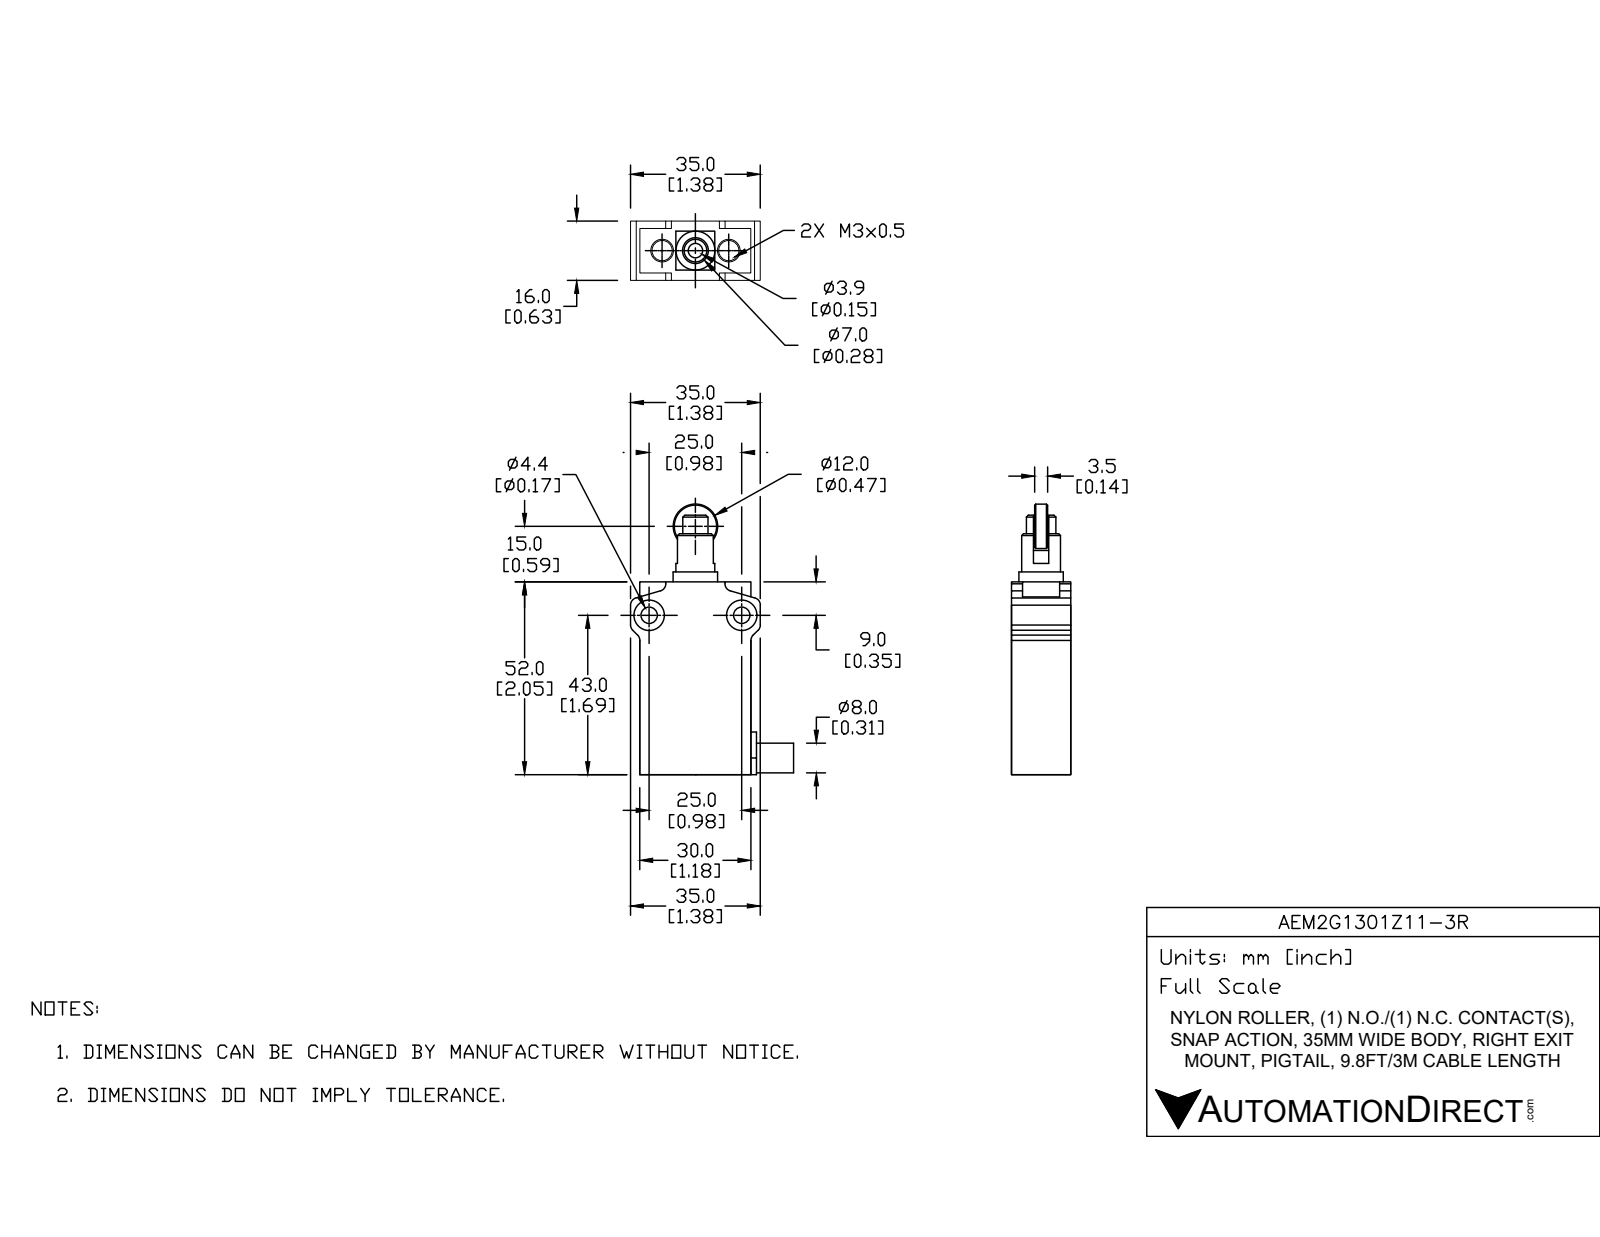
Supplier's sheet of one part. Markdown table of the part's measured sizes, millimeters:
| quantity | value |
| --- | --- |
| part name | AEM2G1301Z11-3R |
| STEP written by | SolidWorks 2017 (AUTOMOTIVE_DESIGN) |
| units | millimeters |
| bodies | 5 solids, 129 faces (64 planar, 52 cylindrical, 13 other) |
| overall size | 70 × 47.5 × 16 |
| volume | 24 840 mm³ |
| surface area | 9 058 mm² |
| round holes (diameter × count) | 3 × 2, 4.4 × 2, 8.2 × 2, 8.1 × 1 |
| round bosses / shafts (diameter × count) | 12 × 2, 10.5 × 1, 8.2 × 1, 8 × 1, 5.6 × 1 |
| partial cylindrical surfaces (radius × count) | 2 × 8, 6.5 × 1 |
| main face-to-face distances | 16, 30, 49, 12, 44.2, 4.8, 5.9, 3.8, 4, 6 |
| hole center spacings | 9.5, 19, 25 |
